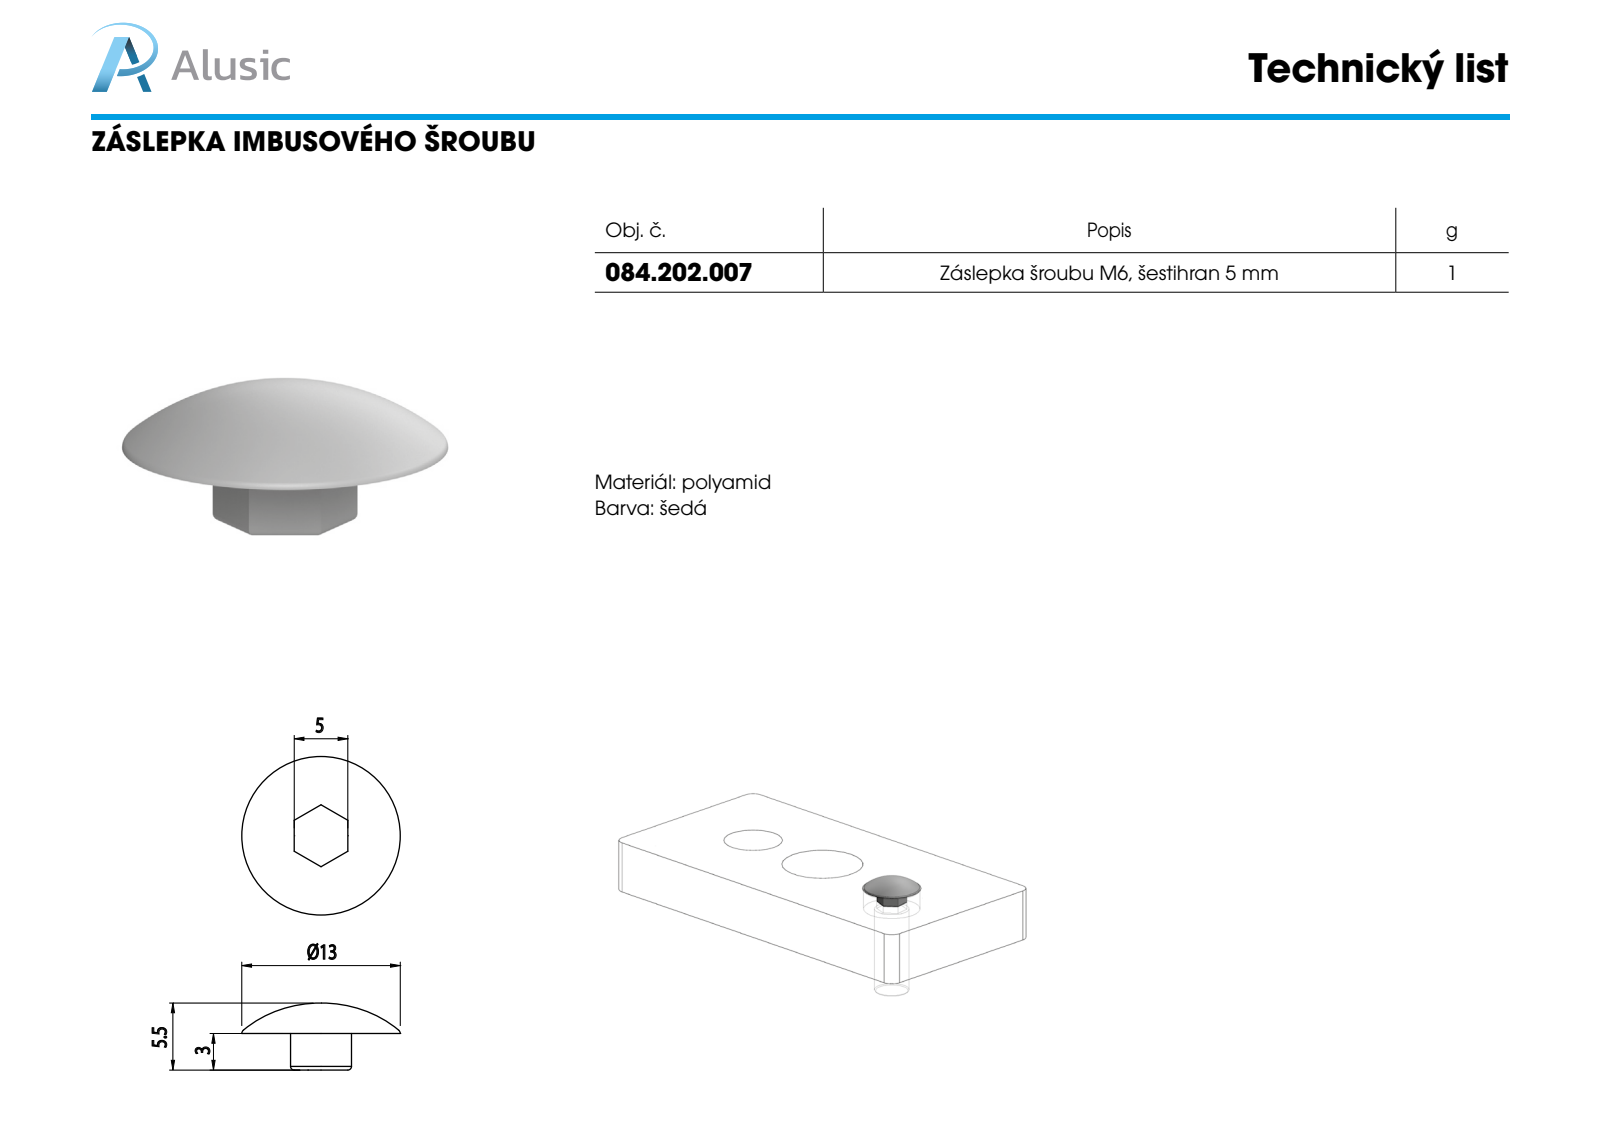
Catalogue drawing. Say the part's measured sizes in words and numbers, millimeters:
The part is named "084.202.007". Its 3-D file was written by "SolidWorks 2011 (CONFIG_CONTROL_DESIGN)". It is 1 solid with 37 faces: 15 planar, 18 cylindrical and 4 other. Overall it measures 13 by 13 by 5.5 millimeters. Its volume is 225 cubic millimeters and its surface area 367 square millimeters. Partial cylindrical surfaces (rounded edges, fillets, slot ends): 18 of radius 0.3. The main face-to-face distances are 1, 4, 5, 3.
